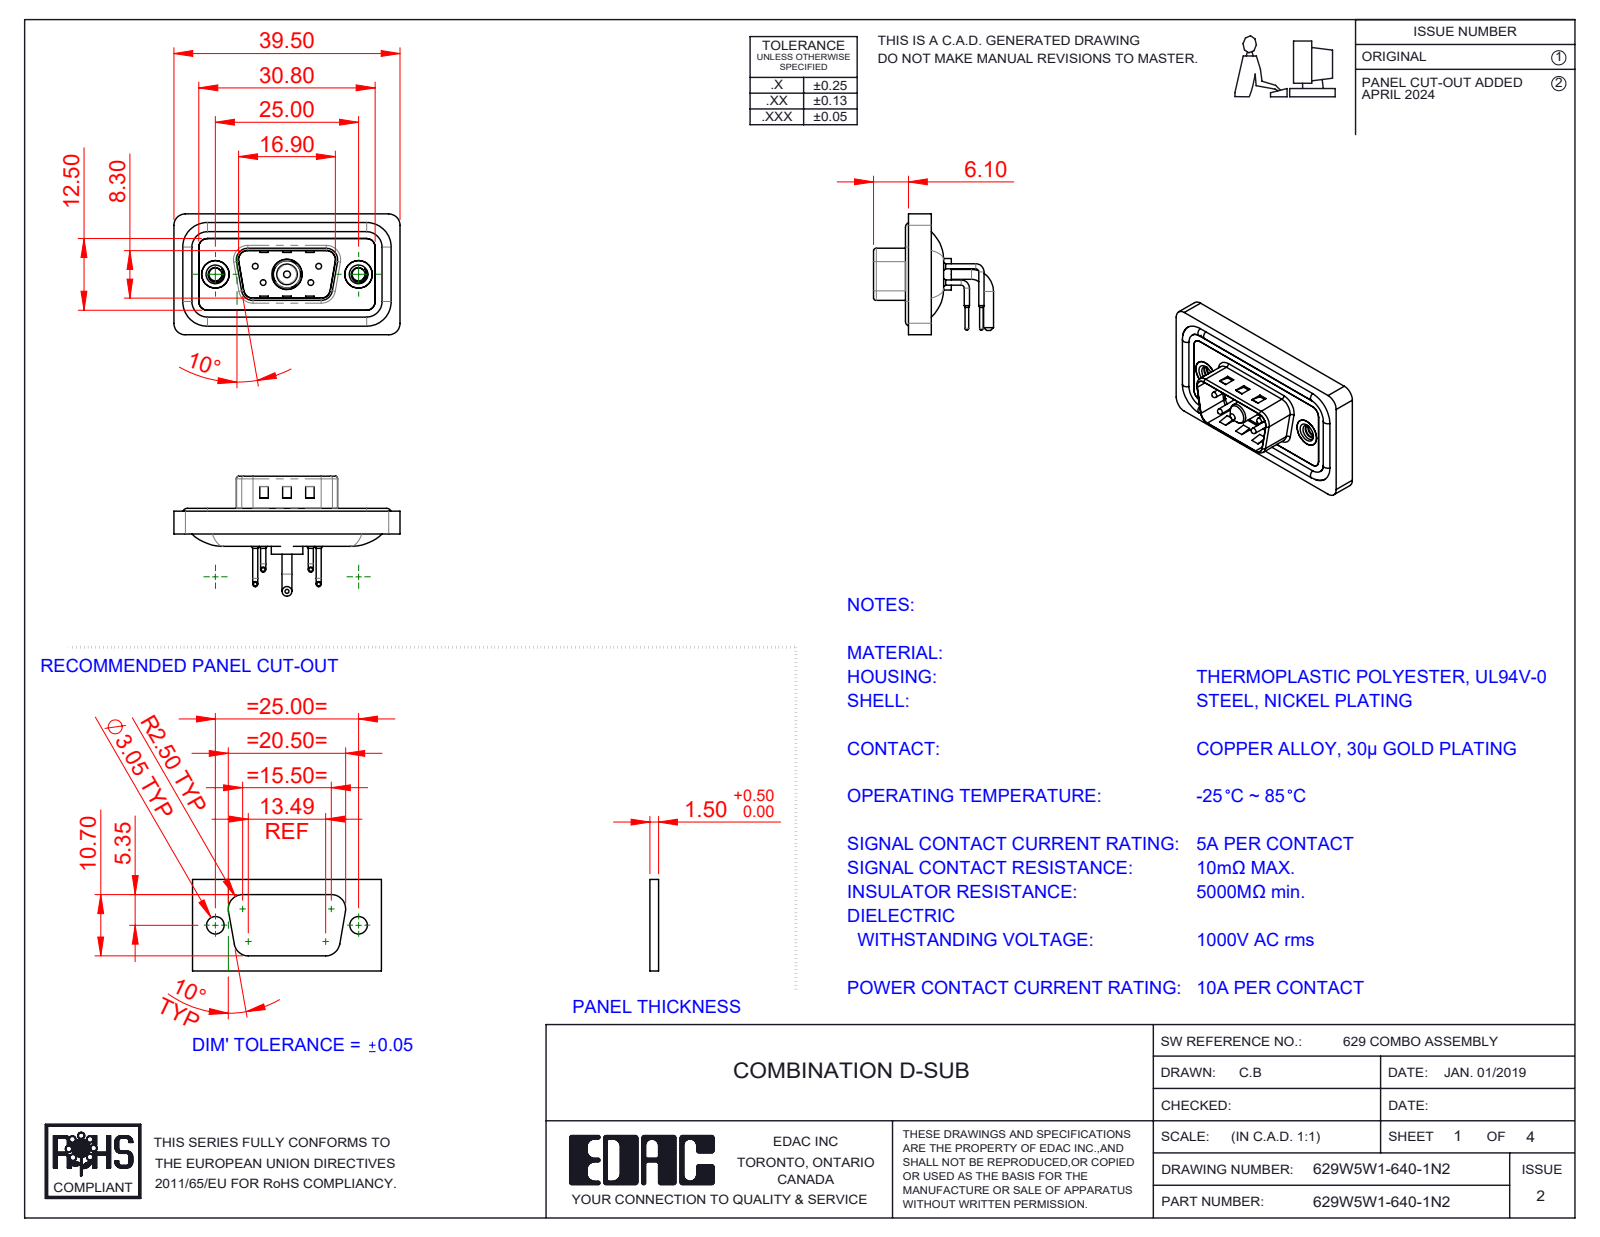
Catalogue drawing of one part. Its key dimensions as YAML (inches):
part_name: "629Combo Waterproof Housing_09 Contacts; Power Pin_10A RA; 629Combo Contact Row 1; 629Combo Shell Front_09 Contacts (+5 more)"
step_written_by: "SolidWorks 2023 (CONFIG_CONTROL_DESIGN)"
units: inches
bodies: {solids: 13, faces: 894, planar: 411, cylindrical: 345, other: 138}
overall_size: [1.555, 0.831, 0.825]
volume: 0.27
surface_area: 11.03
round_holes:
  - {diameter: 0.03, count: 4}
  - {diameter: 0.063, count: 4}
  - {diameter: 0.079, count: 4}
  - {diameter: 0.089, count: 2}
  - {diameter: 0.157, count: 2}
  - {diameter: 0.189, count: 2}
  - {diameter: 0.197, count: 2}
  - {diameter: 0.191, count: 1}
  - {diameter: 0.209, count: 1}
round_bosses_or_shafts:
  - {diameter: 0.035, count: 8}
  - {diameter: 0.063, count: 4}
  - {diameter: 0.059, count: 4}
  - {diameter: 0.039, count: 4}
  - {diameter: 0.026, count: 4}
  - {diameter: 0.193, count: 2}
  - {diameter: 0.067, count: 2}
  - {diameter: 0.217, count: 1}
partial_cylinders:
  - {radius: 0.059, count: 18}
  - {radius: 0.079, count: 18}
  - {radius: 0.02, count: 8}
  - {radius: 0.063, count: 8}
  - {radius: 0.01, count: 4}
  - {radius: 0.024, count: 4}
  - {radius: 0.026, count: 4}
  - {radius: 0.035, count: 4}
face_to_face_distances: [0.016, 0.114, 0.043, 0.031, 0.083, 0.098, 0.063, 0.122, 0.059, 0.177]
hole_center_spacings: [0.124, 0.225, 0.28, 0.492, 0.713, 0.173, 0.173, 0.327]
